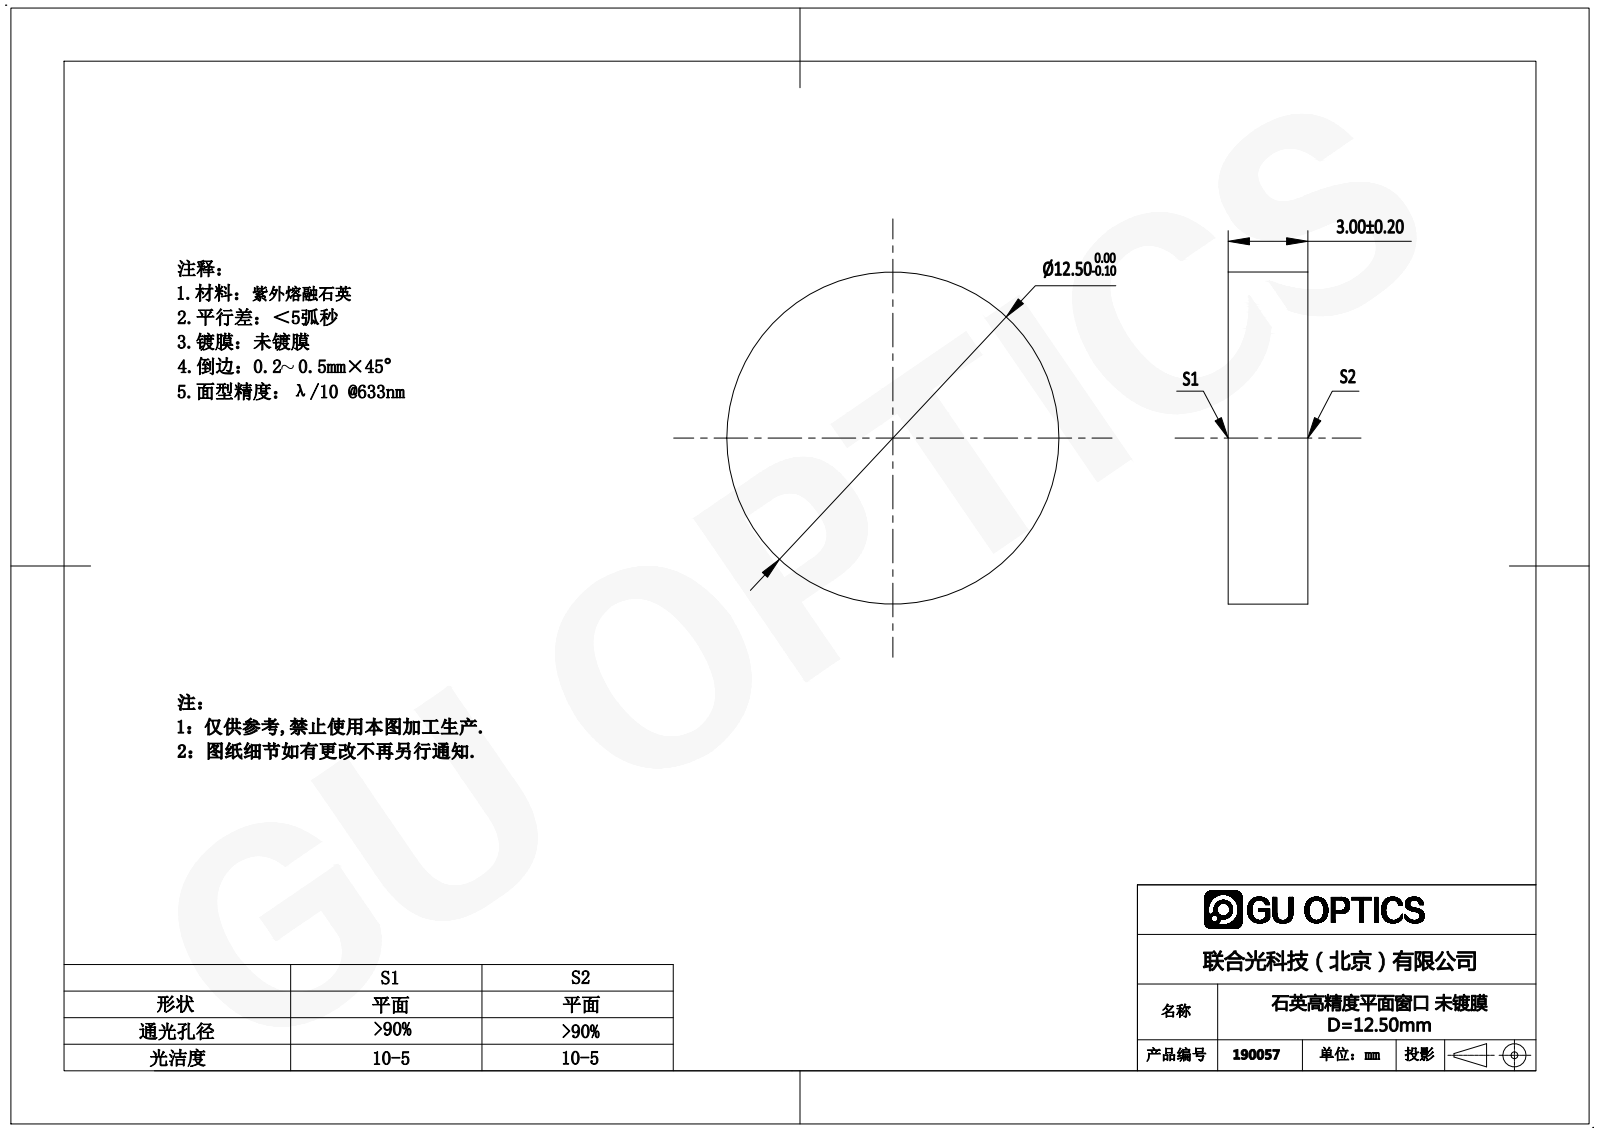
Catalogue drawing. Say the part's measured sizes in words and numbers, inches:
The part is named "190057". Its 3-D file was written by "SolidWorks 2016 (AUTOMOTIVE_DESIGN)". It is 1 solid with 4 faces: 2 planar, 2 cylindrical and 0 other. Overall it measures 0.492 by 0.492 by 0.118 inches. Its volume is 0.022 cubic inches and its surface area 0.563 square inches. Round bosses or shafts: 1 of diameter 0.492. The main face-to-face distances are 0.118.
